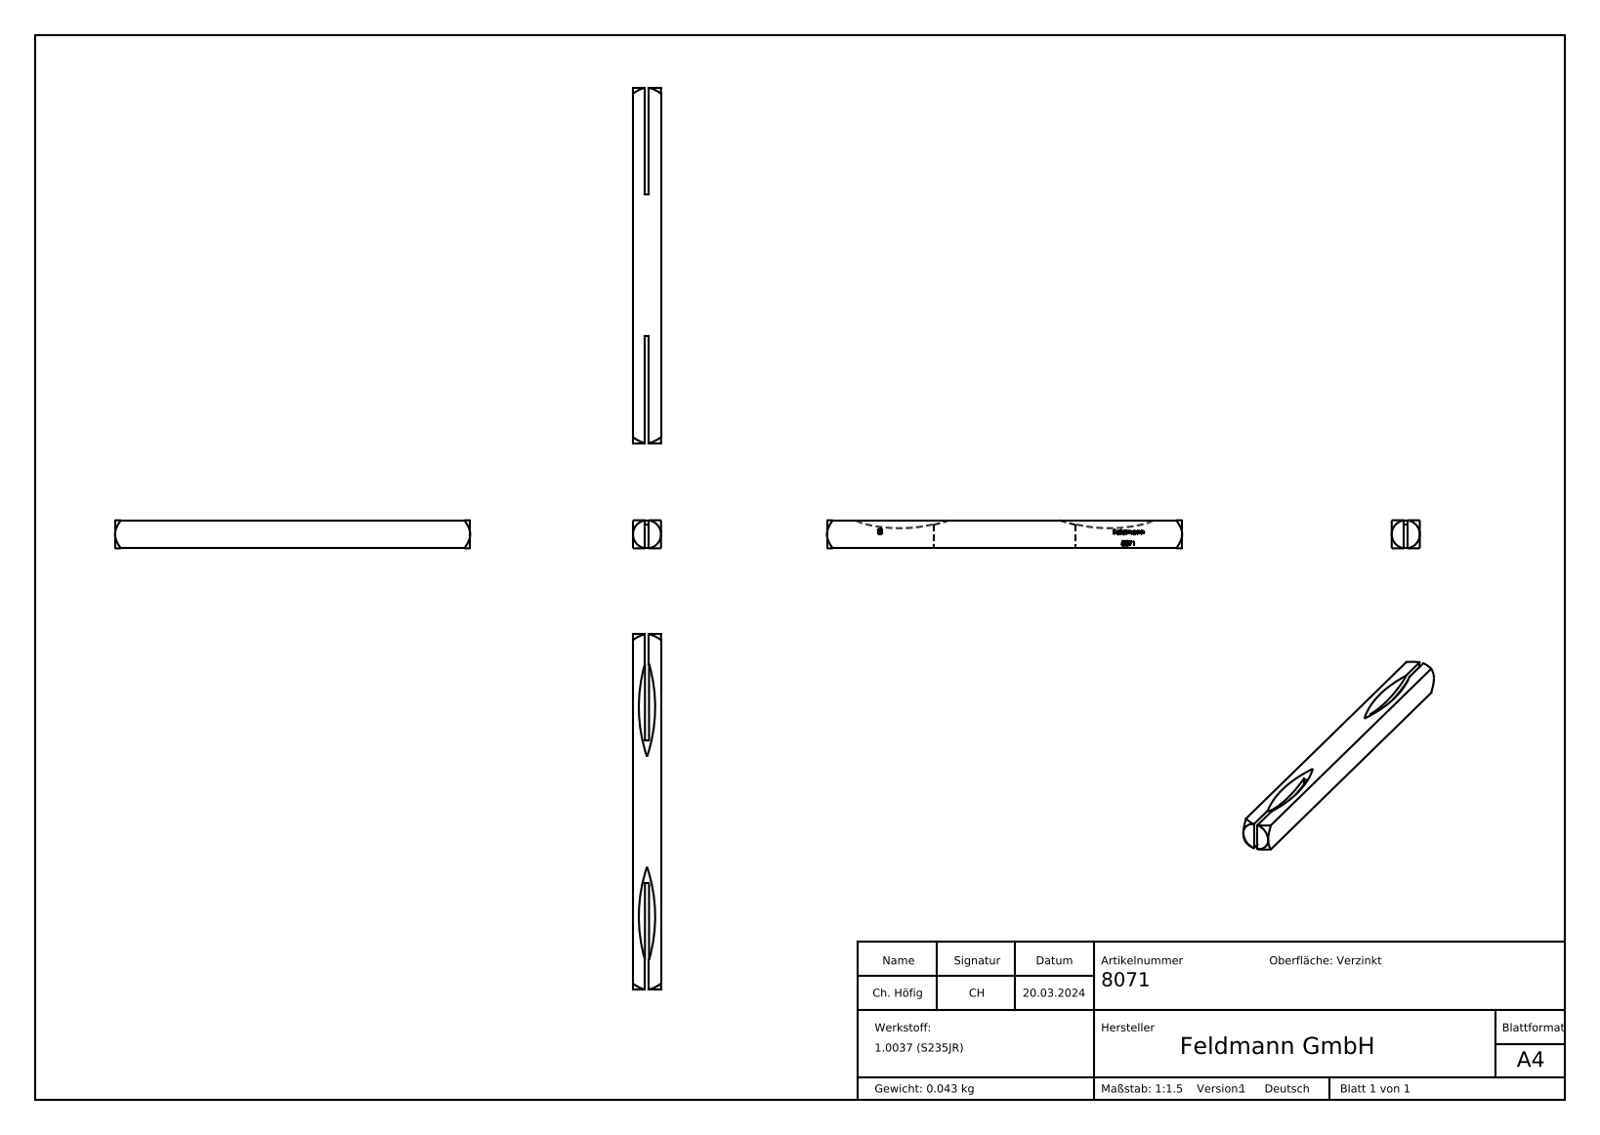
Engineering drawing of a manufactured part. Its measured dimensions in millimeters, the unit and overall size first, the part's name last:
Units: millimetres
Overall size (bounding box): 100 × 7.9 × 7.9
Main face-to-face distances: 7.9, 3.37, 4.53, 3.38, 4.52, 1.15, 100, 30, 70, 40
Volume: 5 522 mm³ · Surface area: 4 023 mm²
Bodies: 1 solid, 225 faces (121 planar, 0 cylindrical, 104 other)
Part name (STEP PRODUCT): 8071
STEP written by: SolidWorks 2018 (CONFIG_CONTROL_DESIGN)
